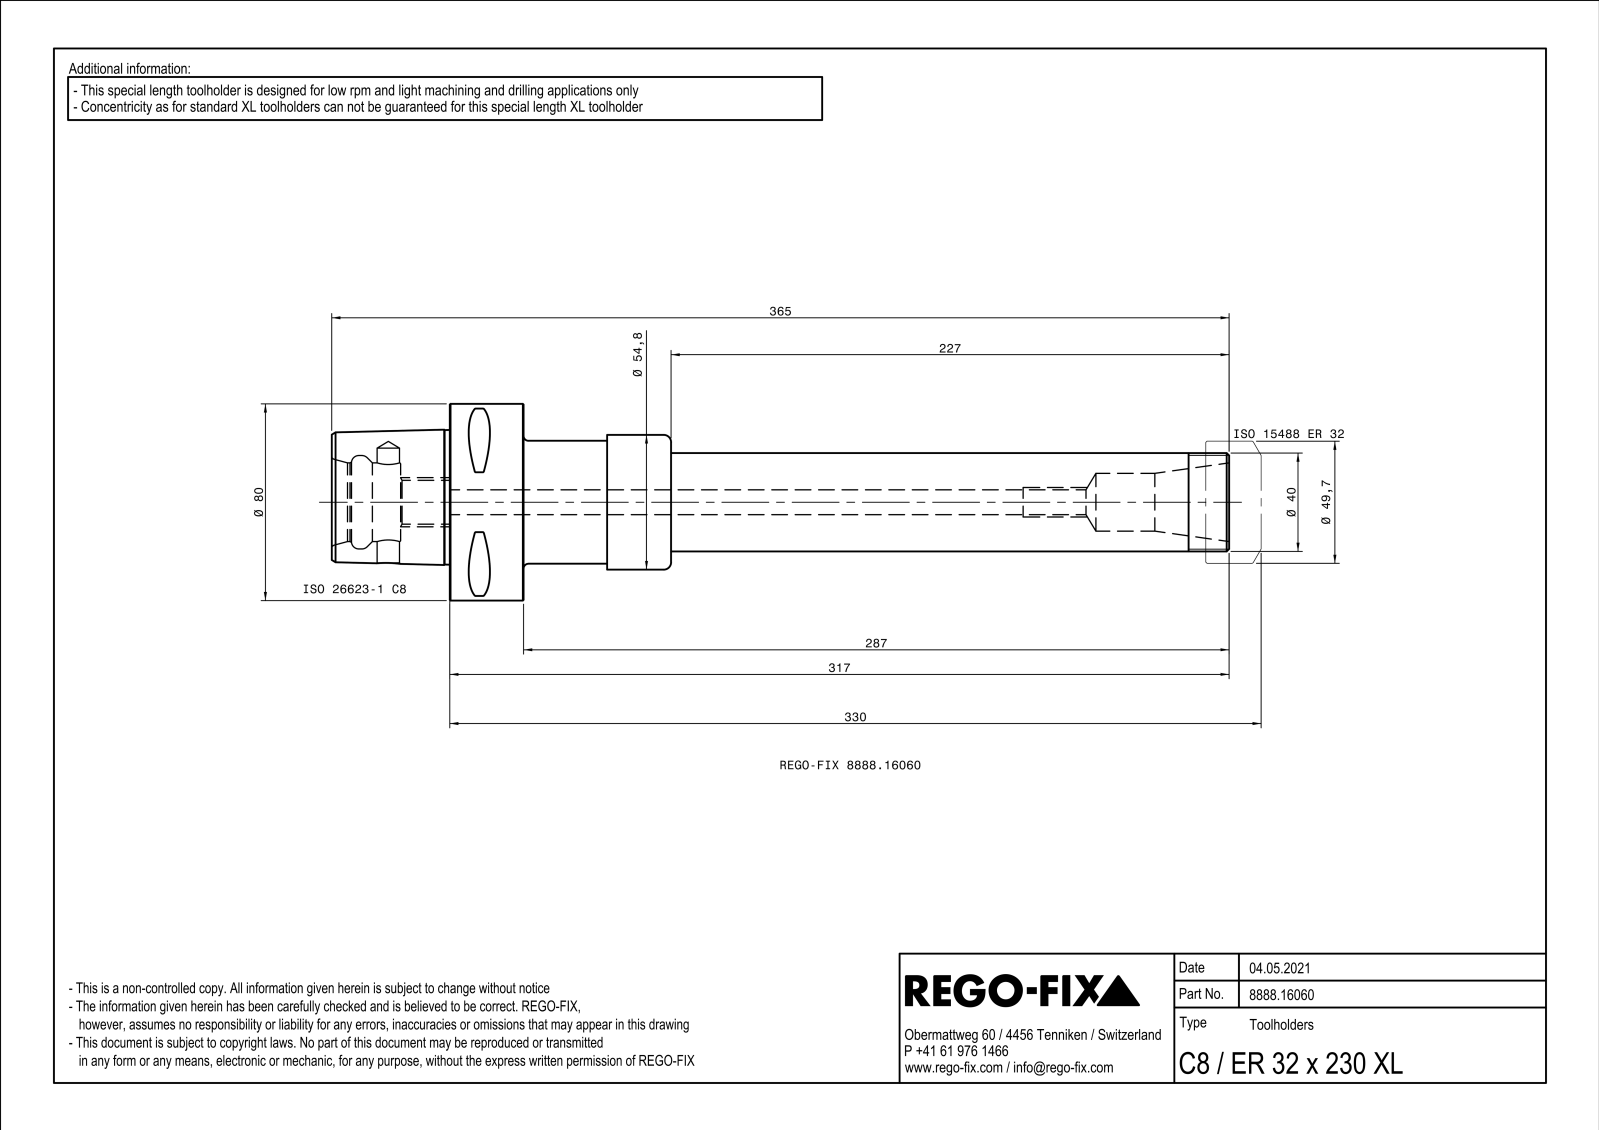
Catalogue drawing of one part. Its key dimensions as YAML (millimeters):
part_name: "NOCUT"
step_written_by: "SIEMENS PLM Software Solid Edge ST10 (AUTOMOTIVE_DESIGN)"
units: millimeters
bodies: {solids: 1, faces: 149, planar: 30, cylindrical: 33, other: 86}
overall_size: [265, 80, 80]
volume: 452087
surface_area: 77662
round_holes:
  - {diameter: 4, count: 1}
  - {diameter: 9.1, count: 1}
  - {diameter: 10.1, count: 1}
  - {diameter: 10.11, count: 1}
  - {diameter: 13, count: 1}
  - {diameter: 17.84, count: 1}
  - {diameter: 23.5, count: 1}
  - {diameter: 32, count: 1}
  - {diameter: 33, count: 1}
  - {diameter: 38, count: 1}
  - {diameter: 40.2, count: 1}
  - {diameter: 48.38, count: 1}
round_bosses_or_shafts:
  - {diameter: 80, count: 1}
  - {diameter: 54.8, count: 1}
  - {diameter: 50, count: 1}
  - {diameter: 45, count: 1}
  - {diameter: 42, count: 1}
  - {diameter: 40, count: 1}
  - {diameter: 31.6, count: 1}
  - {diameter: 30.5, count: 1}
partial_cylinders:
  - {radius: 0.5, count: 8}
face_to_face_distances: [30, 78, 48, 52, 59.99, 89.99, 137.99, 50, 7.99, 82]
hole_center_spacings: [37]
